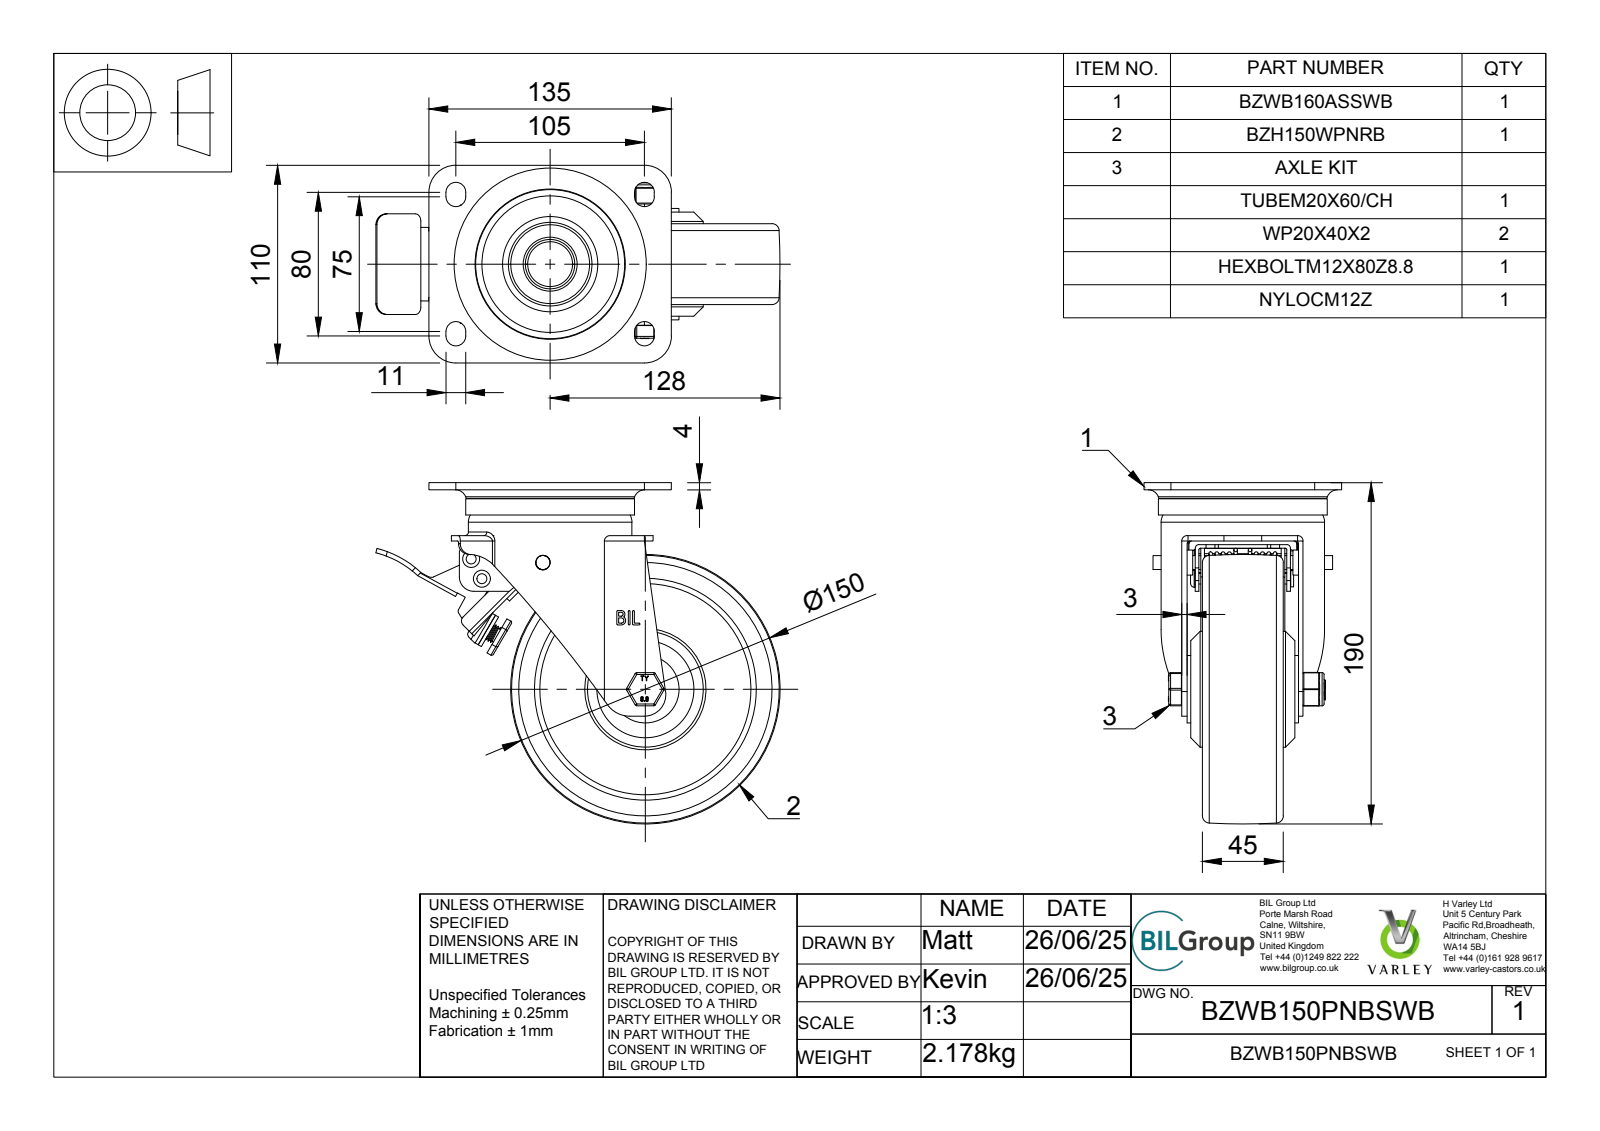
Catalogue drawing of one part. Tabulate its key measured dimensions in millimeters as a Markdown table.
| quantity | value |
| --- | --- |
| part name | BZWB150PNBSWB v2; BZWB160ASSWB v1; ZINC PLATED, PRESSED STEEL TOP PLATE; ZINC PLATED, PRESSED STEEL FORKS (+8 more) |
| STEP written by | Autodesk Translation Framework v14.10.0.0 (AUTOMOTIVE_DESIGN) |
| units | millimeters |
| bodies | 36 solids, 838 faces (423 planar, 290 cylindrical, 125 other) |
| overall size | 225 × 190 × 110 |
| volume | 741 124 mm³ |
| surface area | 285 354 mm² |
| round holes (diameter × count) | 4 × 2, 6 × 2, 8 × 1, 8.5 × 1, 10 × 1, 12 × 1, 12.2 × 1, 12.5 × 1, 14 × 1, 20.5 × 1, 21 × 1, 30 × 1 |
| round bosses / shafts (diameter × count) | 5 × 10, 2 × 10, 9.5 × 2, 9 × 2, 5.9 × 2, 94 × 1, 91 × 1, 70 × 1 |
| partial cylindrical surfaces (radius × count) | 1 × 23, 0.5 × 18, 1.5 × 15, 3 × 12, 2 × 9, 5.5 × 8, 15 × 4, 6 × 3 |
| main face-to-face distances | 2, 14, 53.5, 3, 4, 6.5, 28, 11, 11.5, 36.5 |
| hole center spacings | 12.53, 35.17, 40.05, 90.66, 109.83, 121.1 |
